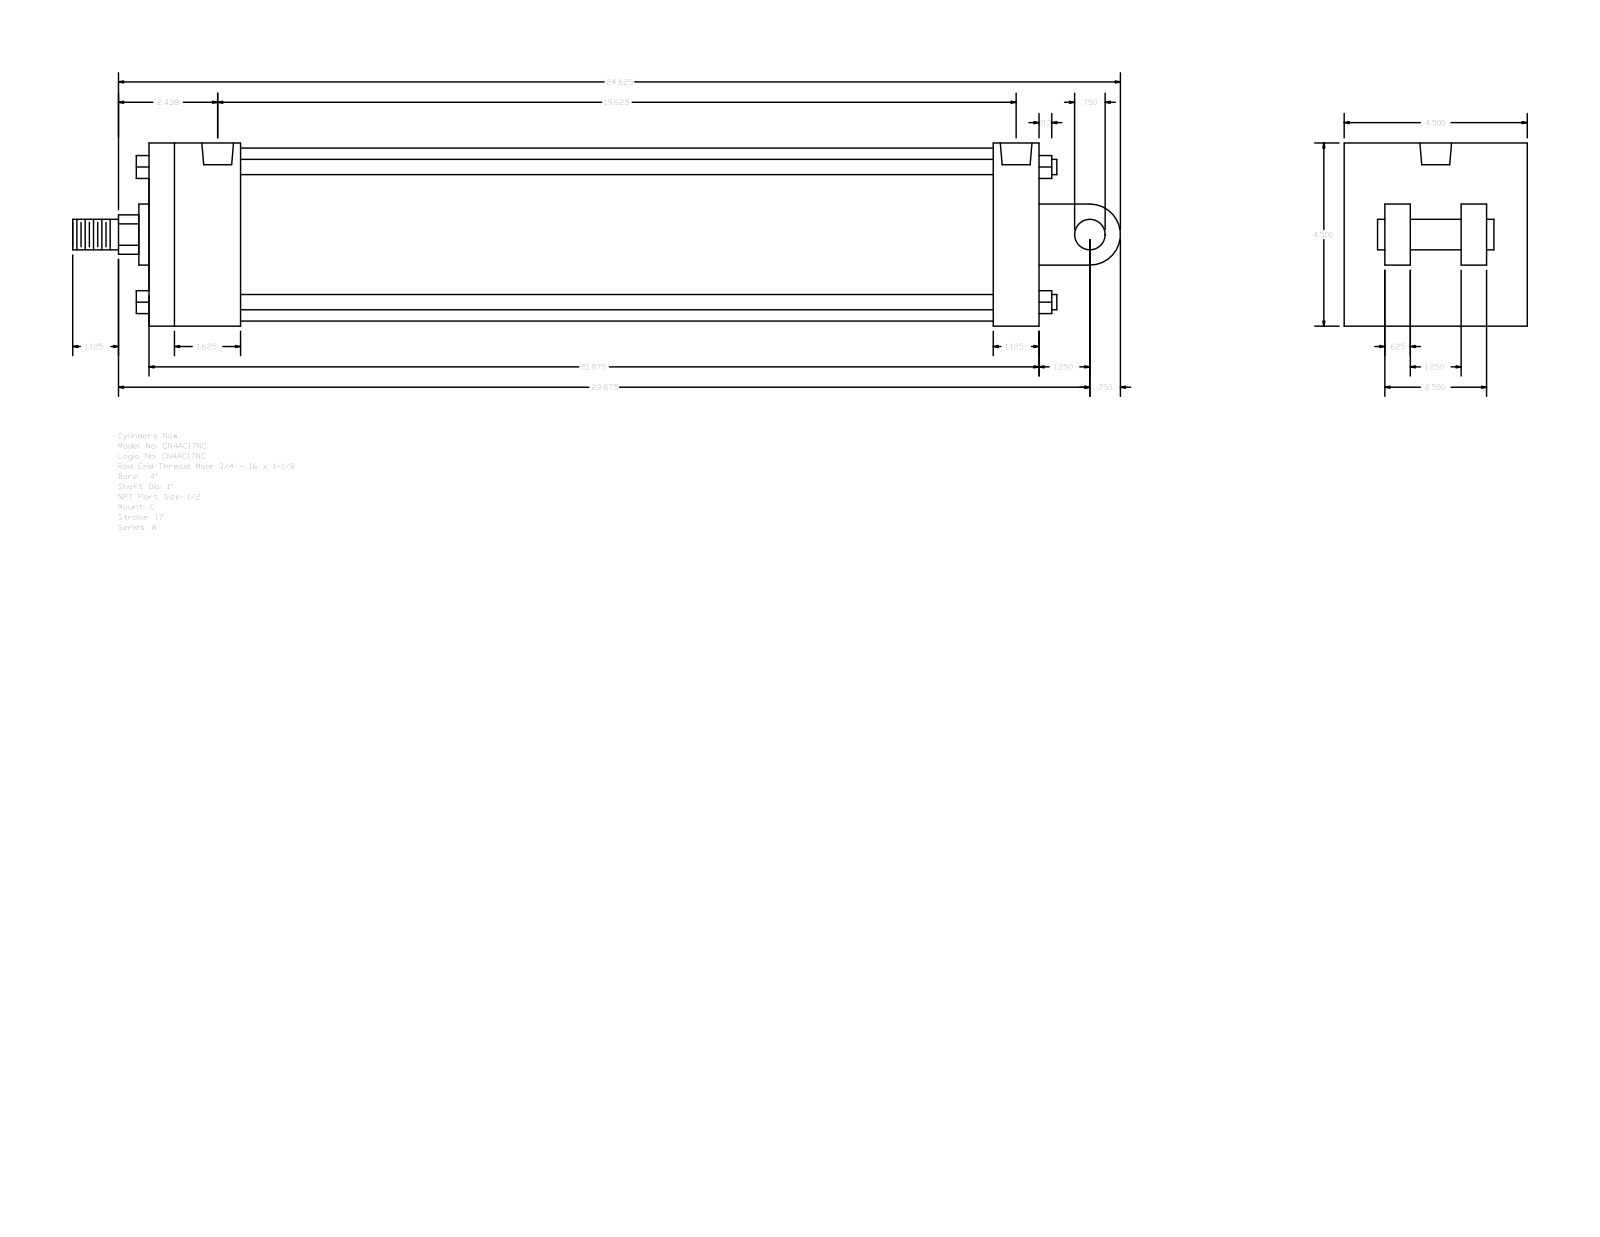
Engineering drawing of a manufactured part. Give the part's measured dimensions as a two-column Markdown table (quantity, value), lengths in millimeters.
| quantity | value |
| --- | --- |
| part name | A_C__0400_1 |
| STEP written by | GSSL Pune (CONFIG_CONTROL_DESIGN) |
| units | millimeters |
| bodies | 0 solids, 135 faces (102 planar, 33 cylindrical, 0 other) |
| overall size | 654.05 × 114.3 × 114.3 |
| round holes (diameter × count) | 8.73 × 4, 19.77 × 2 |
| round bosses / shafts (diameter × count) | 9.53 × 4, 19.05 × 2, 107.95 × 1, 38.1 × 1, 25.4 × 1 |
| partial cylindrical surfaces (radius × count) | 12.29 × 1, 19.05 × 1 |
| main face-to-face distances | 114.3, 555.62, 73.03, 28.57, 527.05, 57.15, 469.9, 498.47, 41.27, 38.1 |
| hole center spacings | 3.18, 492.12, 495.3, 498.48 |
